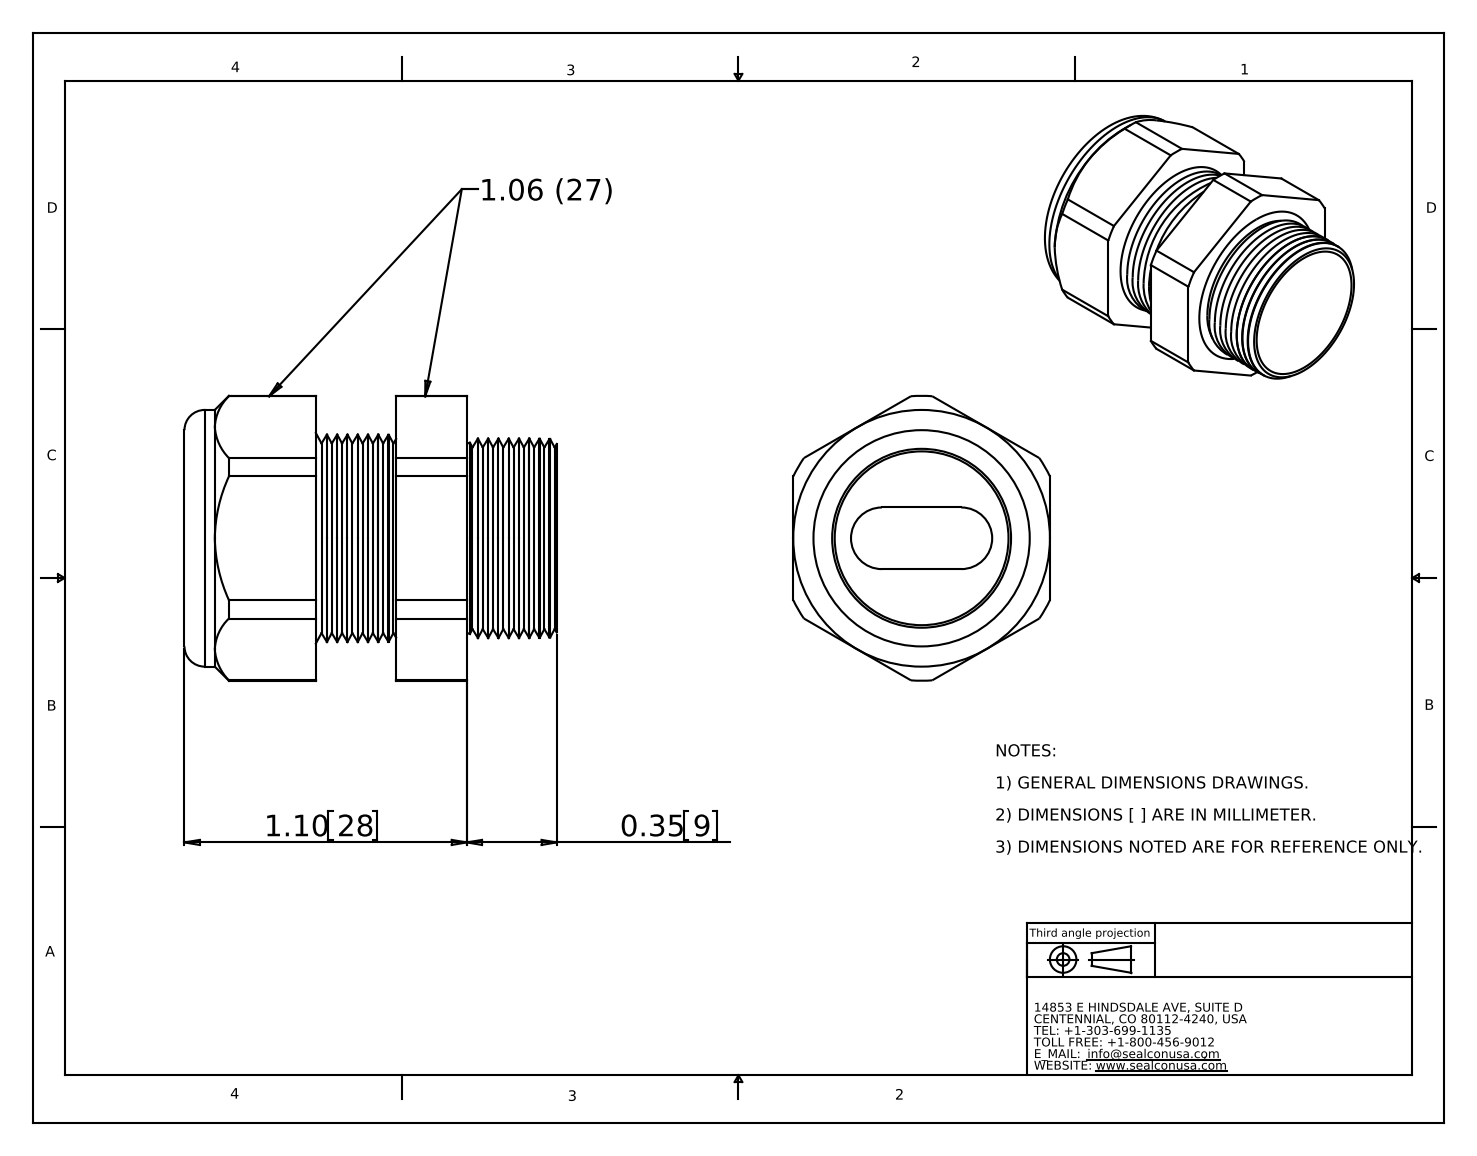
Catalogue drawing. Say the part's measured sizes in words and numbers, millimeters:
The part is named "CD16NS-01". Its 3-D file was written by "SolidWorks 2007 (CONFIG_CONTROL_DESIGN)". It is 2 solids with 133 faces: 21 planar, 20 cylindrical and 92 other. Overall it measures 36.8 by 28.2 by 25.4 millimeters. Its volume is 8 190 cubic millimeters and its surface area 8 006 square millimeters. Round holes: 1 of diameter 17.7. Round bosses or shafts: 1 of diameter 25.4, 1 of diameter 17.2. Partial cylindrical surfaces (rounded edges, fillets, slot ends): 2 of radius 3, 1 of radius 14.1. The main face-to-face distances are 25.4, 20.9, 13, 8, 27.9, 14.9, 7, 10, 3, 10.9.
